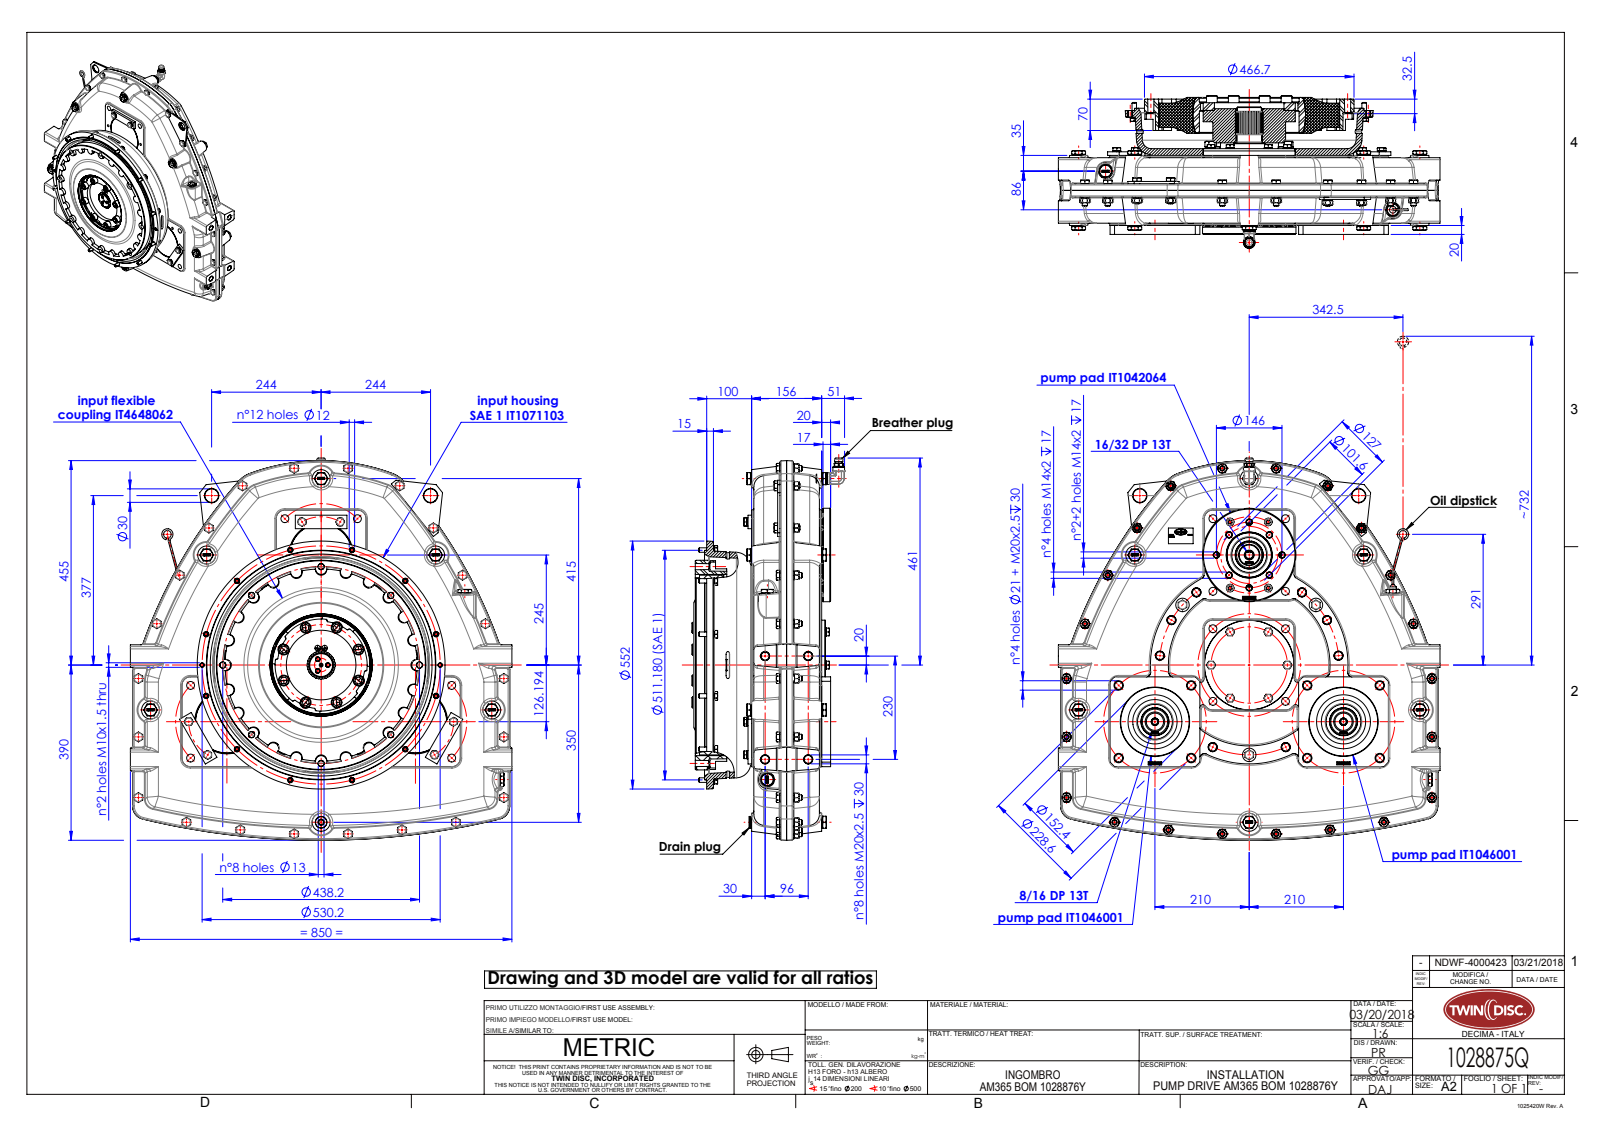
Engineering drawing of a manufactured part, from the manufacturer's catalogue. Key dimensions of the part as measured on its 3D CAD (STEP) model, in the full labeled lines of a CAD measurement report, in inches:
Part name (STEP PRODUCT): IT4648062_rev00-installation; ITam365-005_rev00-installation; ITam365-014_rev00-installation; ITam365-006_rev00-installation (+8 more)
STEP written by: SolidWorks 2015 (AUTOMOTIVE_DESIGN)
Units: inches
Bodies: 175 solids, 10308 faces (4291 planar, 2673 cylindrical, 3344 other)
Overall size (bounding box): 33.496 × 33.465 × 13.394
Volume: 5 390 in³ · Surface area: 10 350 in²
Round holes (diameter × count): ⌀0.512 ×36, ⌀0.689 ×30, ⌀0.335 ×29, ⌀0.472 ×27, ⌀0.827 ×26, ⌀0.48 ×25, ⌀0.402 ×24, ⌀0.406 ×21, ⌀0.551 ×20, ⌀0.433 ×14, ⌀0.669 ×13, ⌀0.733 ×10
Round bosses / shafts (diameter × count): ⌀0.394 ×29, ⌀0.831 ×25, ⌀0.709 ×25, ⌀0.713 ×24, ⌀0.638 ×24, ⌀0.472 ×21, ⌀0.63 ×16, ⌀1.063 ×10
Partial cylindrical surfaces — rounded edges, fillets, slot ends (radius × count): R0.492 ×72, R0.014 ×58, R0.018 ×58, R1.04 ×58, R1.163 ×58, R0.079 ×54, R0.098 ×46, R0.118 ×44
Main face-to-face distances: 3.071, 2.874, 5.945, 0.197, 0.591, 3.661, 5.748, 0.787, 6.142, 6.732
Hole centre spacings: 13.638, 32.047, 3.274, 11.703, 9.257, 1.783, 2.591, 2.953
